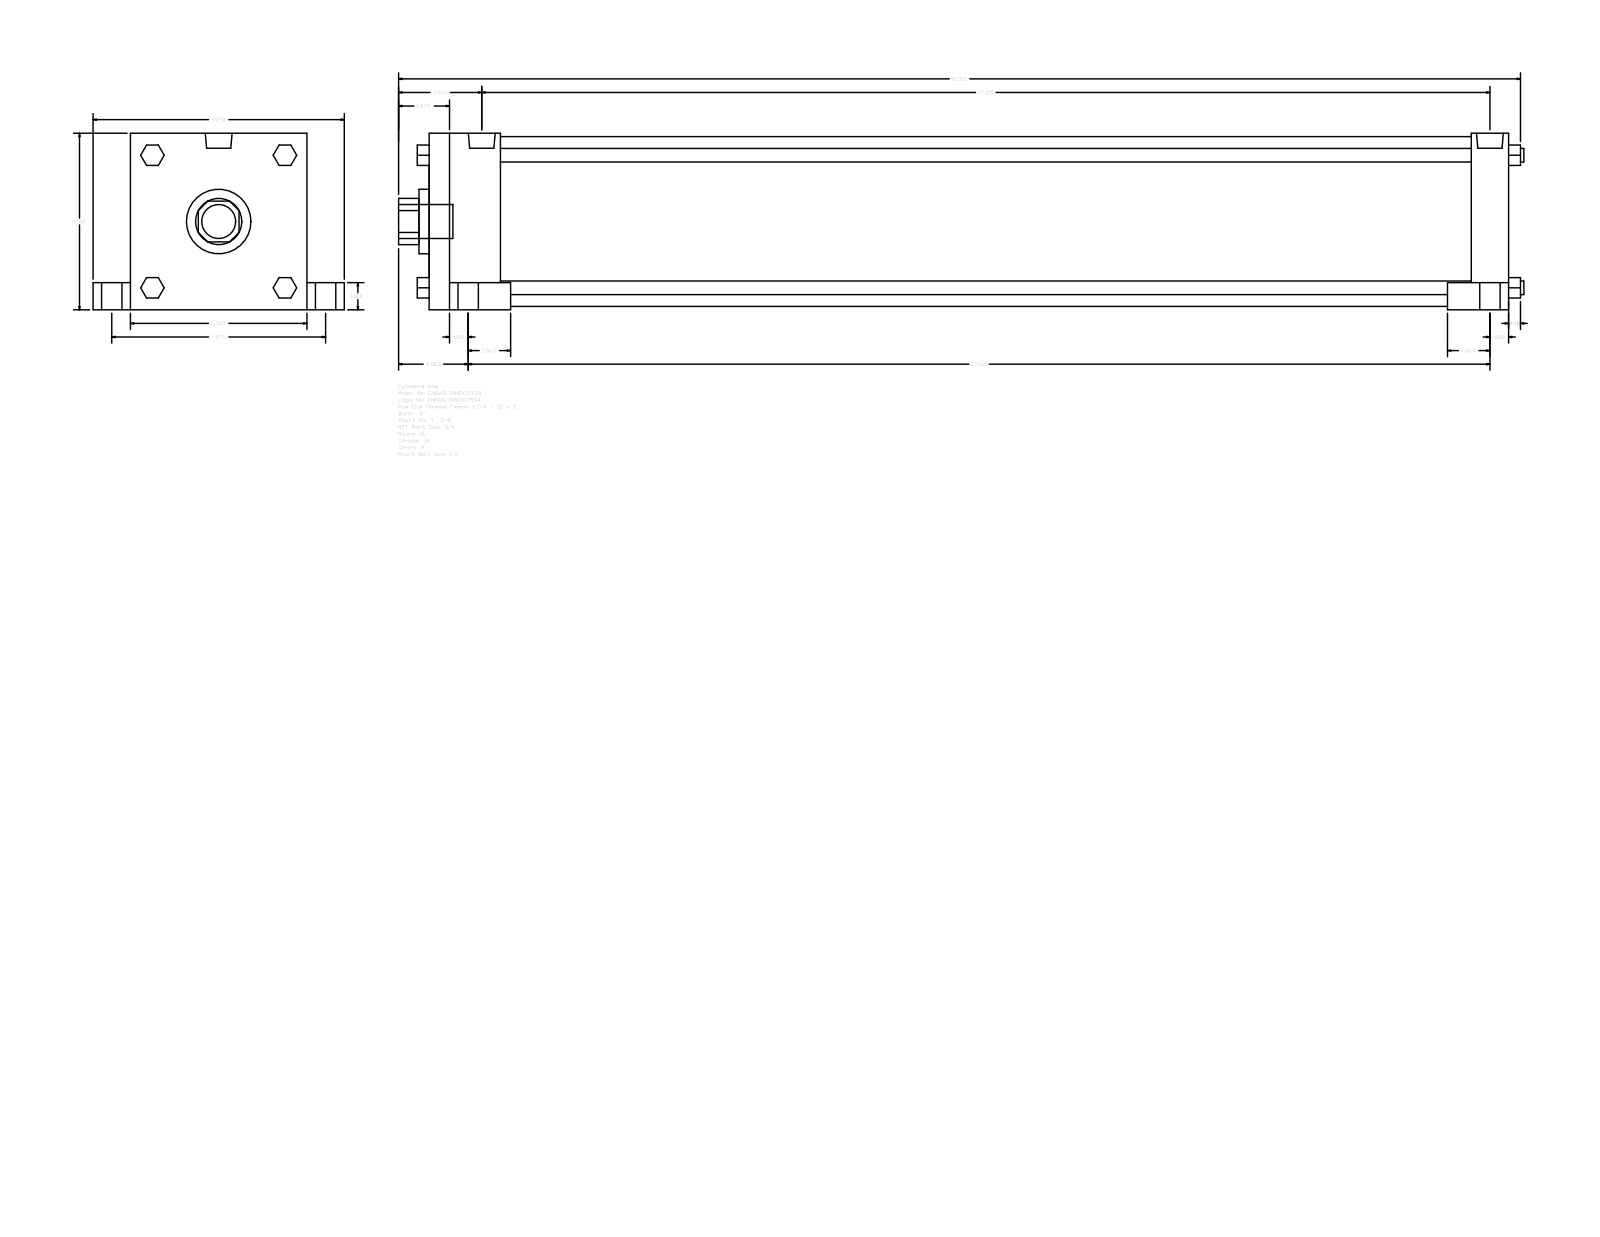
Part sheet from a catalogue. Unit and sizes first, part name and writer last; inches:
Units: inches
Overall size (bounding box): 41.437 × 9.25 × 6.5
Round holes (diameter × count): ⌀1.75 ×1, ⌀2.375 ×1, ⌀6.25 ×1
Round bosses / shafts (diameter × count): ⌀1 ×4, ⌀0.75 ×4, ⌀0.594 ×4, ⌀0.5 ×4, ⌀0.989 ×2, ⌀1.25 ×1
Partial cylindrical surfaces — rounded edges, fillets, slot ends (radius × count): R0.852 ×1
Main face-to-face distances: 6.5, 39.75, 1.375, 2.625, 37.125, 38.375, 35.75, 1, 5.5, 7.875
Bodies: 0 solids, 150 faces (114 planar, 36 cylindrical, 0 other)
Part name (STEP PRODUCT): A_SL__0600_1.75
STEP written by: GSSL Pune (CONFIG_CONTROL_DESIGN)
